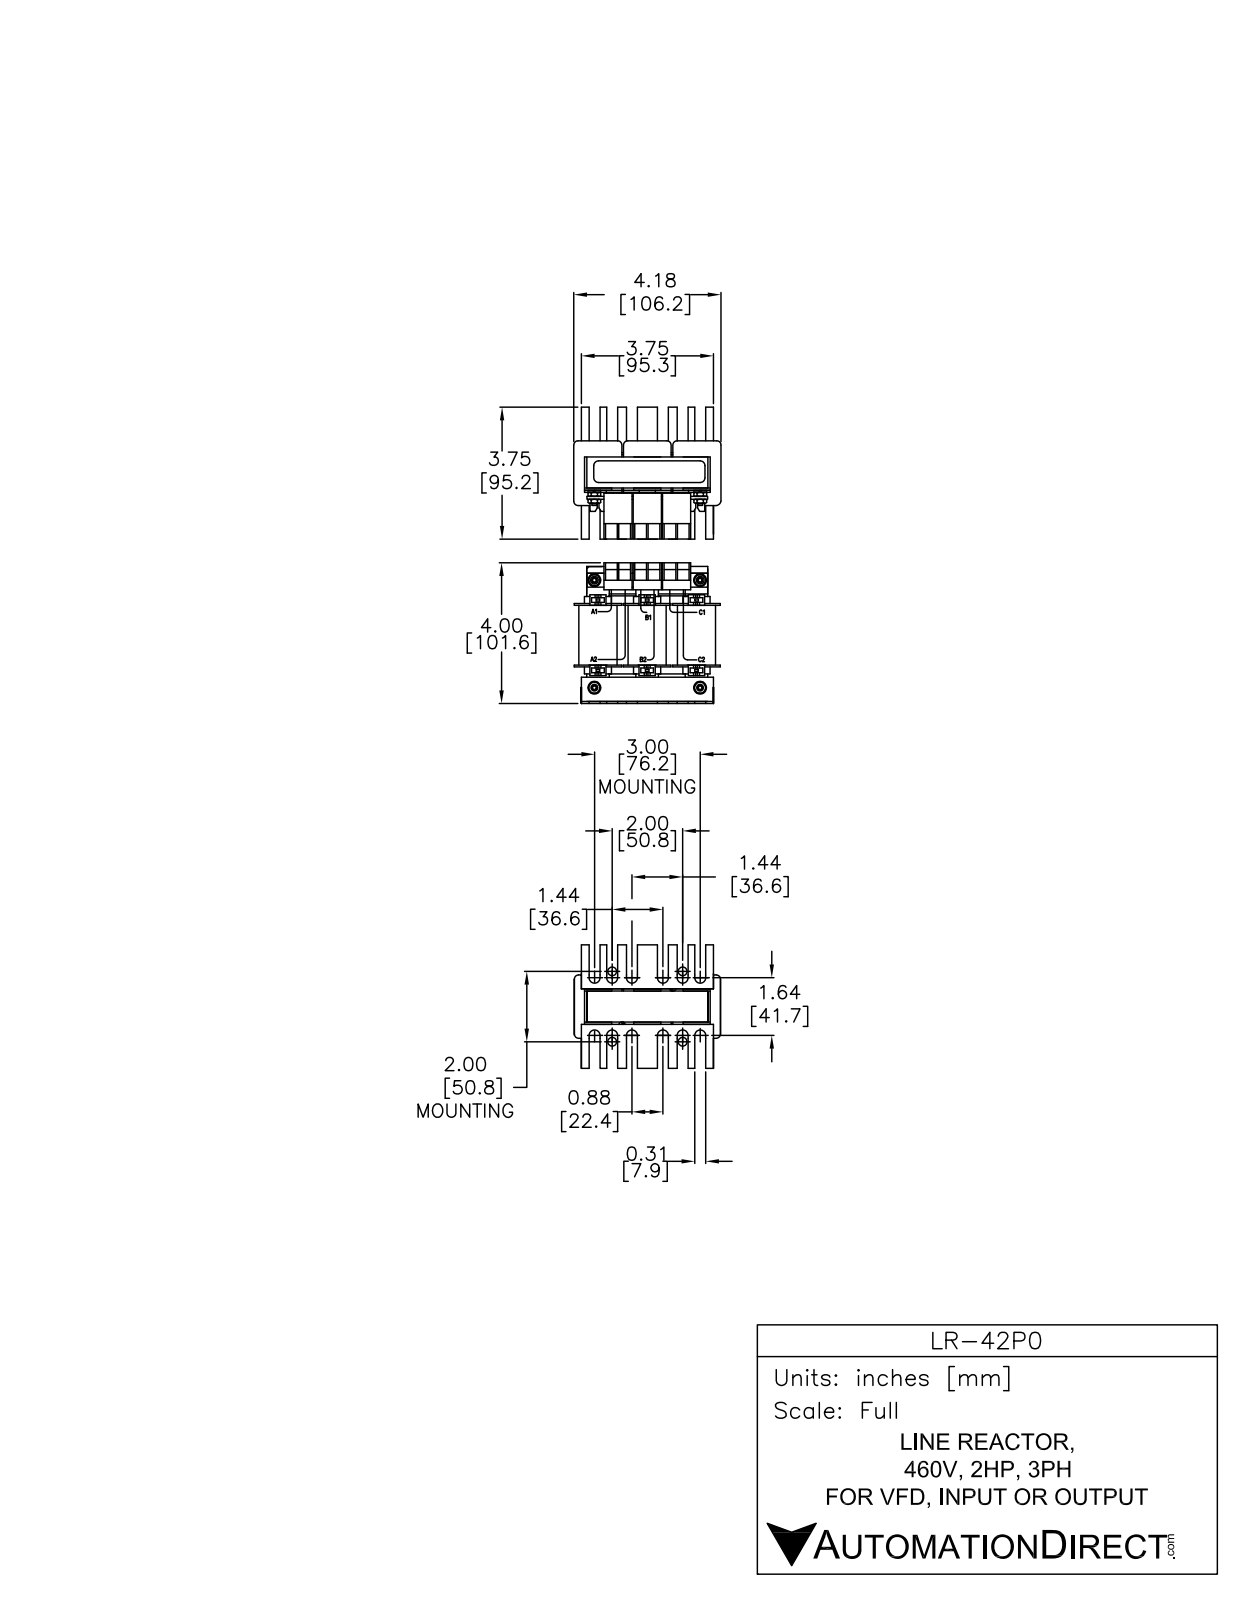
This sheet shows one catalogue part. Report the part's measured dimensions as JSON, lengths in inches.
{"part_name": "LR-42P0", "step_written_by": "SolidWorks 2011 (AUTOMOTIVE_DESIGN)", "units": "inches", "bodies": {"solids": 17, "faces": 941, "planar": 743, "cylindrical": 198, "other": 0}, "overall_size": [4.144, 3.874, 3.514], "volume_in3": 16.62, "surface_area_in2": 153.8, "round_bosses_or_shafts": [[0.305, 4], [0.138, 4]], "partial_cylinders_radius": [[0.157, 50], [0.072, 24], [0.315, 12], [0.118, 6], [0.034, 3], [0.049, 2]], "face_to_face_distances": [0.197, 0.846, 0.108, 2.008, 1.033, 1.043, 0.295, 1.142, 2.795, 0.098]}
